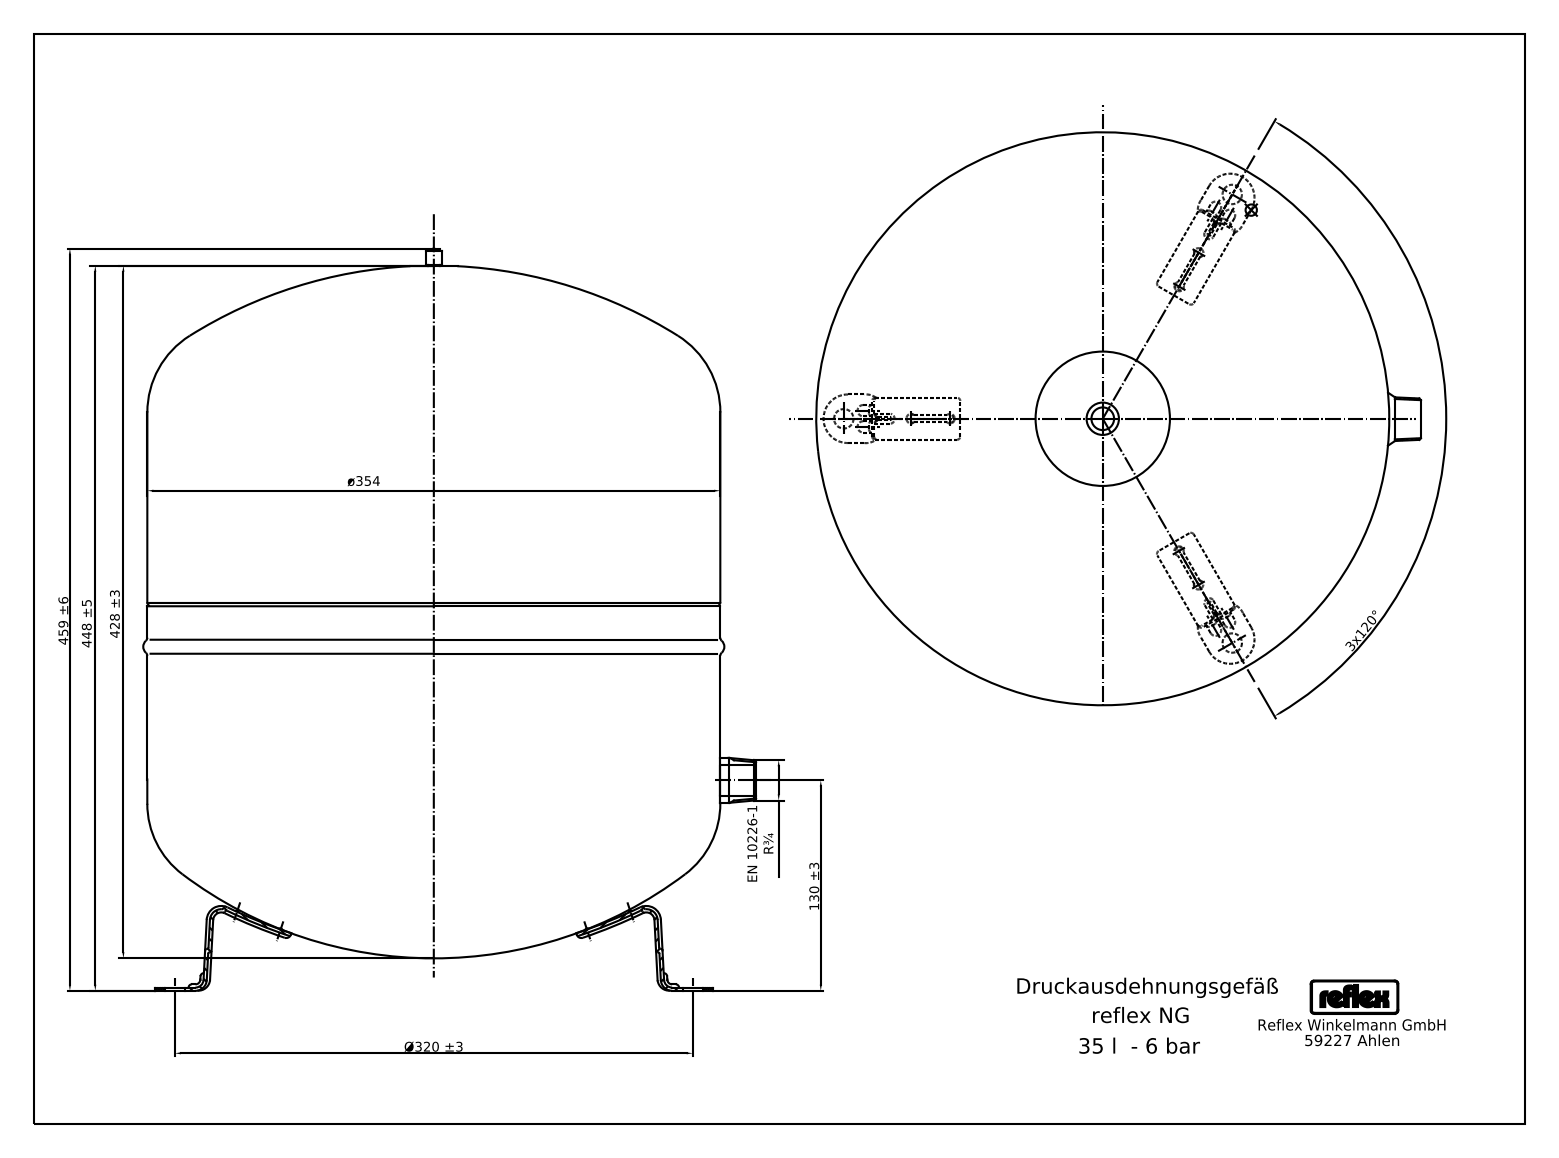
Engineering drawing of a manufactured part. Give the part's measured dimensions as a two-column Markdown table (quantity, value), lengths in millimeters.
| quantity | value |
| --- | --- |
| STEP written by | Mechanical Desktop 2011 (CONFIG_CONTROL_DESIGN) |
| units | millimeters |
| bodies | 16 solids, 191 faces (76 planar, 74 cylindrical, 41 other) |
| overall size | 460 × 390 × 376 |
| volume | 35 710 000 mm³ |
| surface area | 1 024 000 mm² |
| round holes (diameter × count) | 15 × 3, 20.5 × 1 |
| round bosses / shafts (diameter × count) | 376 × 1, 354 × 1, 26.9 × 1, 13 × 1, 7.8 × 1 |
| partial cylindrical surfaces (radius × count) | 148.38 × 9, 150.38 × 9, 15 × 6, 2.81 × 4, 1.12 × 3, 1.92 × 2, 3.38 × 2, 4.64 × 2 |
| main face-to-face distances | 242.6, 113.3, 129.3, 16, 110.2, 223.5, 239.5, 352.8, 2, 112.2 |
| hole center spacings | 277.13, 277.12 |
